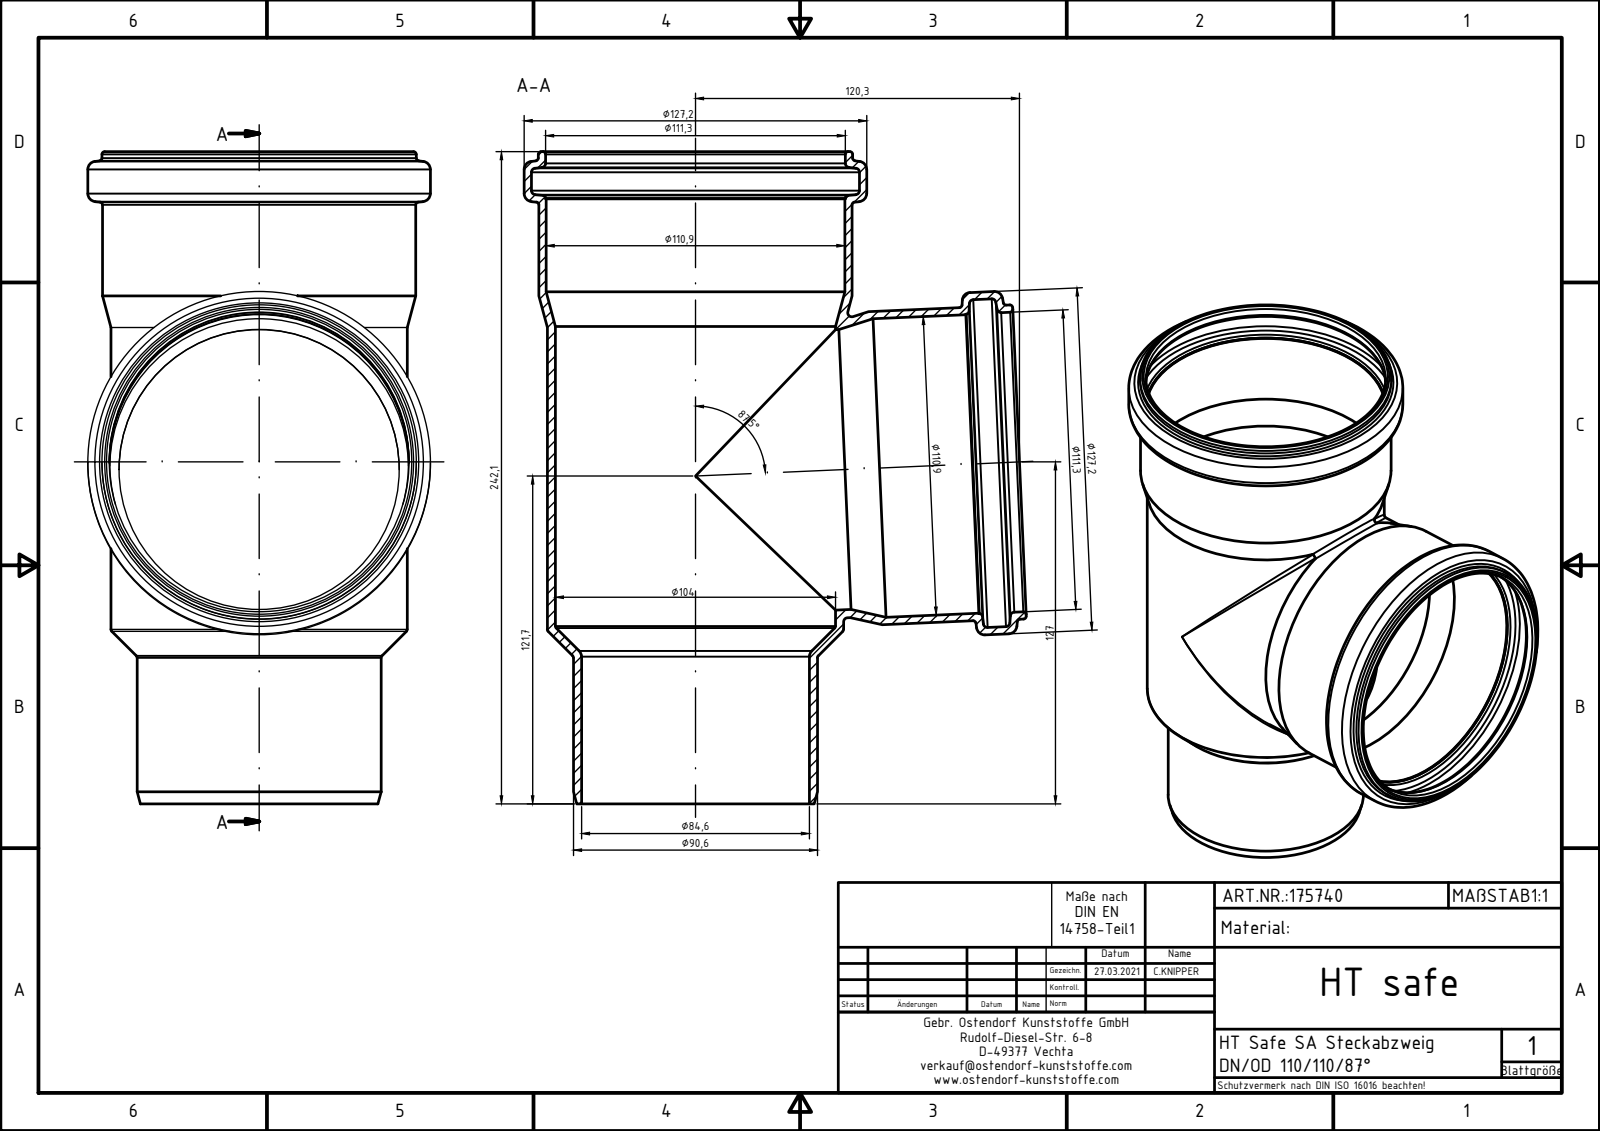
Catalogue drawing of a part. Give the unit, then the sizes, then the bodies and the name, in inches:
Units: inches
Overall size (bounding box): 9.531 × 7.338 × 5.008
Round holes (diameter × count): ⌀4.382 ×3, ⌀4.094 ×2, ⌀4.366 ×2, ⌀4.795 ×2, ⌀3.331 ×1
Round bosses / shafts (diameter × count): ⌀5.008 ×2, ⌀4.594 ×2, ⌀4.579 ×2, ⌀4.331 ×2, ⌀3.567 ×1
Main face-to-face distances: 9.531, 0.689, 8.843
Volume: 18.62 in³ · Surface area: 329.8 in²
Bodies: 1 solid, 68 faces (5 planar, 20 cylindrical, 43 other)
Part name (STEP PRODUCT): 175740 HT safe SA Steckabzweig DN110x110x87,5°
STEP written by: Autodesk Inventor 2020 (AUTOMOTIVE_DESIGN)
